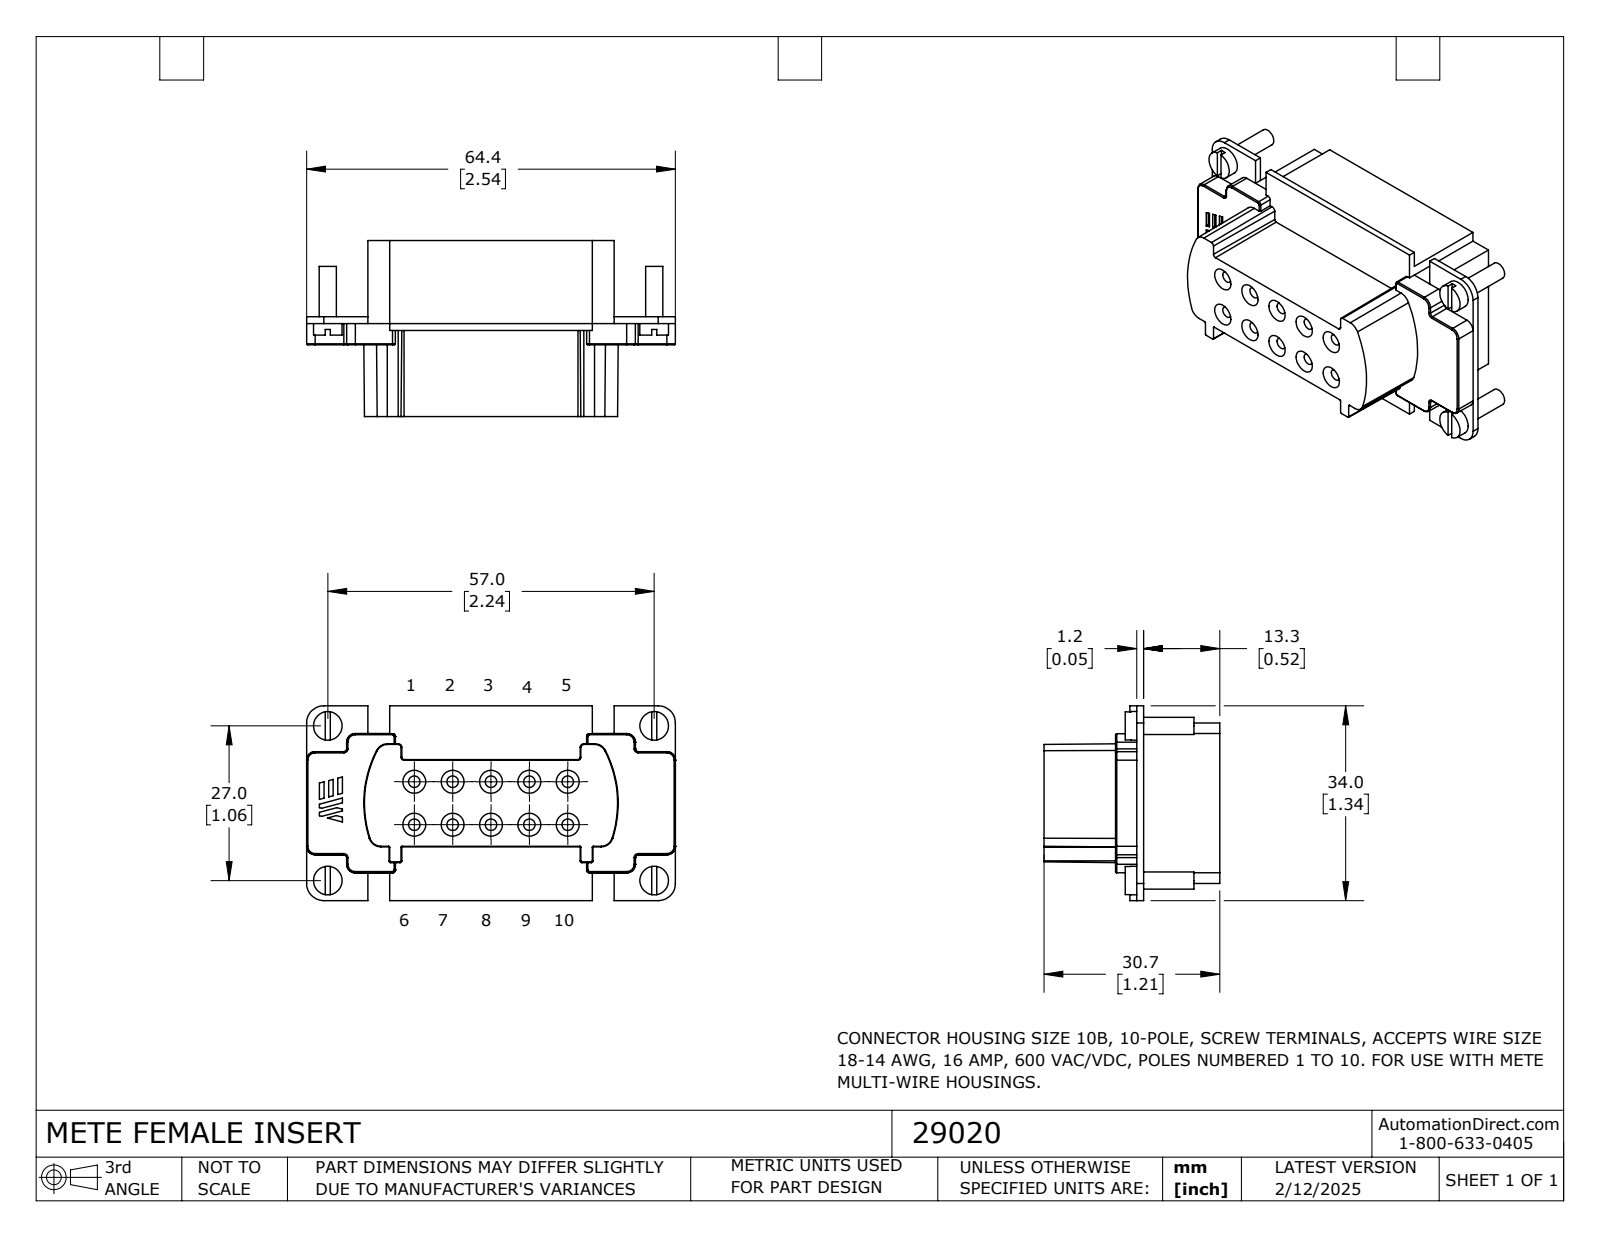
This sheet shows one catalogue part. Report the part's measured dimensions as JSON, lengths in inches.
{"part_name": "29020", "step_written_by": "SolidWorks 2024 (CONFIG_CONTROL_DESIGN)", "units": "inches", "bodies": {"solids": 1, "faces": 256, "planar": 127, "cylindrical": 58, "other": 71}, "overall_size": [2.536, 1.339, 1.209], "volume_in3": 1.894, "surface_area_in2": 17.1, "round_holes": [[0.079, 10]], "round_bosses_or_shafts": [[0.197, 4], [0.118, 4]], "partial_cylinders_radius": [[0.008, 10], [0.118, 4]], "face_to_face_distances": [0.047, 0.524, 0.094, 0.618, 1.209, 0.685, 0.591, 1.102, 0.571, 0.717], "hole_center_spacings": [0.264, 0.396, 0.528, 0.605, 0.295, 0.791, 0.844, 1.055]}
